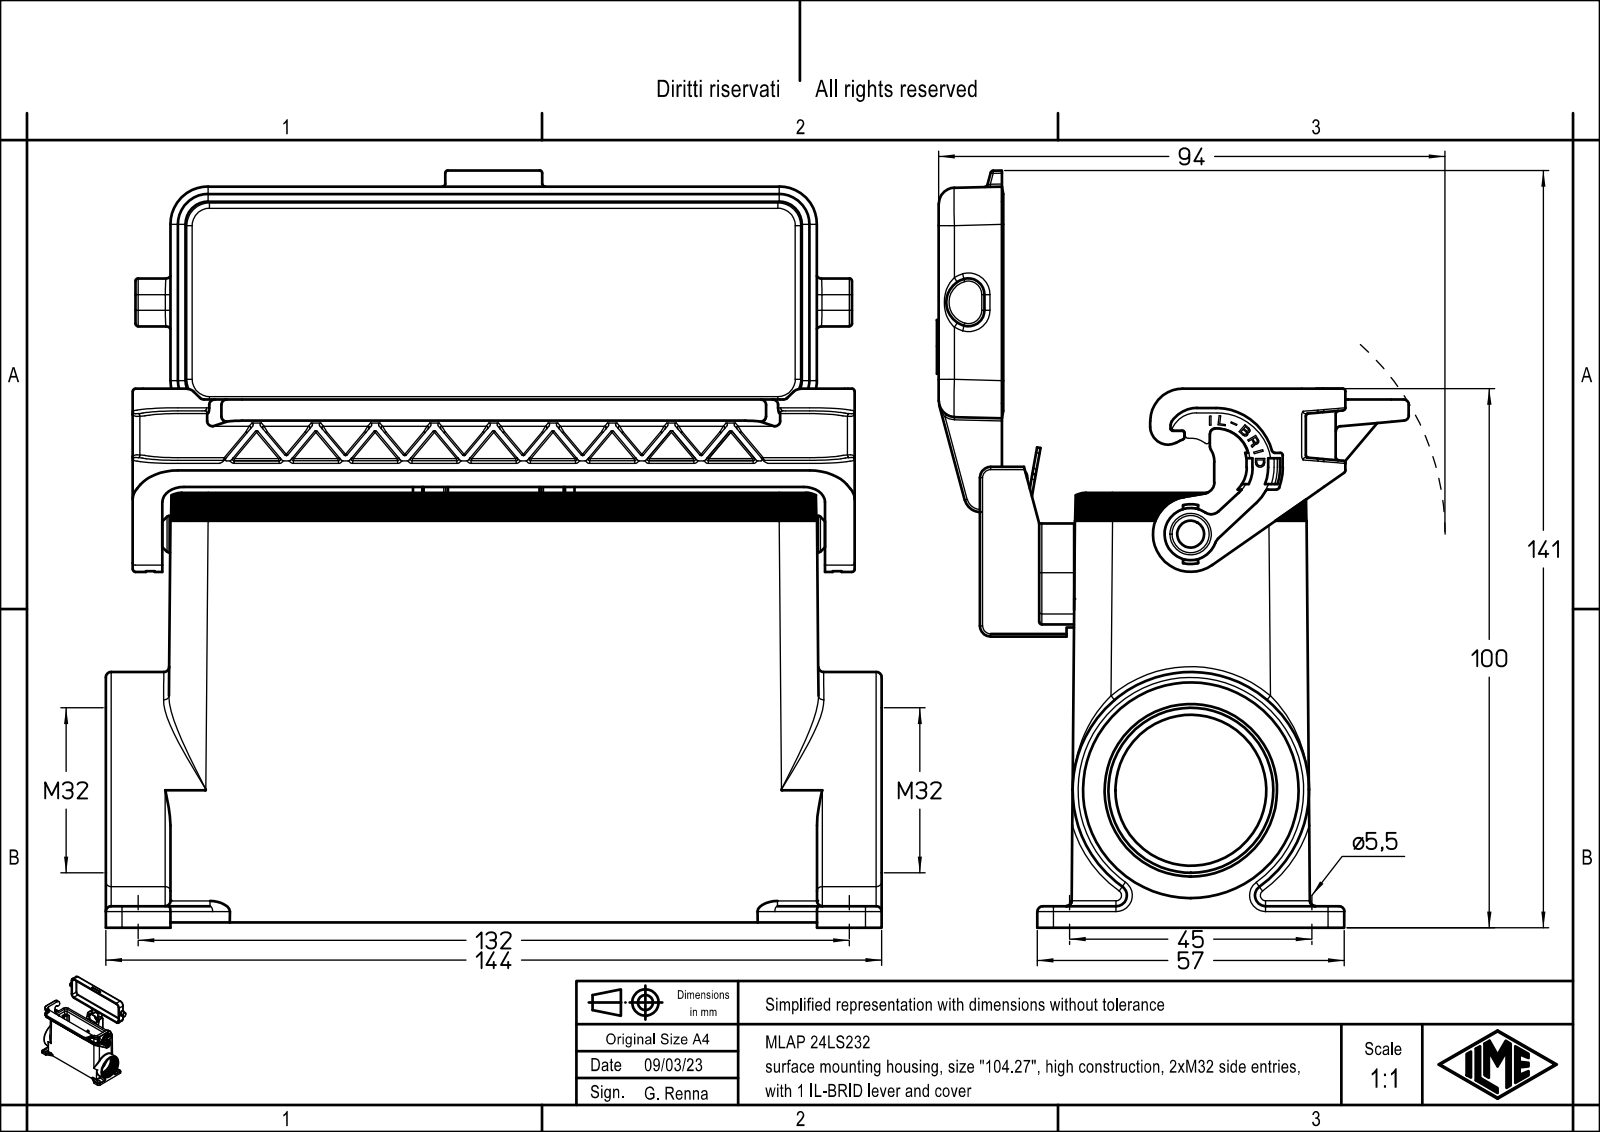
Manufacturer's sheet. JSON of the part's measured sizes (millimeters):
{"part_name": "MLAP 24 LS40; MLAP 24LS232", "step_written_by": "Creo Elements/Direct Modeling 20.1B 02-Apr-2019 (C) Parametric Technology GmbH (AUTOMOTIVE_DESIGN)", "units": "millimeters", "bodies": {"solids": 1, "faces": 1366, "planar": 831, "cylindrical": 404, "other": 131}, "overall_size": [144, 140.49, 87.76], "volume_mm3": 200069, "surface_area_mm2": 103301, "round_holes": [[3, 4], [3.5, 4], [5.5, 4], [3.25, 1], [5.4, 1], [7.7, 1], [28, 1], [30.5, 1]], "round_bosses_or_shafts": [[43.87, 1], [8.4, 1], [6.9, 1], [6.8, 1], [5.2, 1], [3.2, 1]], "partial_cylinders_radius": [[0.5, 29], [0.1, 27], [1, 24], [0.2, 23], [3, 23], [0.17, 17], [0.33, 16], [2, 15]], "face_to_face_distances": [2, 3, 2.8, 69.71, 71.71, 7, 97, 94, 4, 1], "hole_center_spacings": [16.64, 38.63, 118.34, 123.37, 27, 45, 104, 107.45]}
